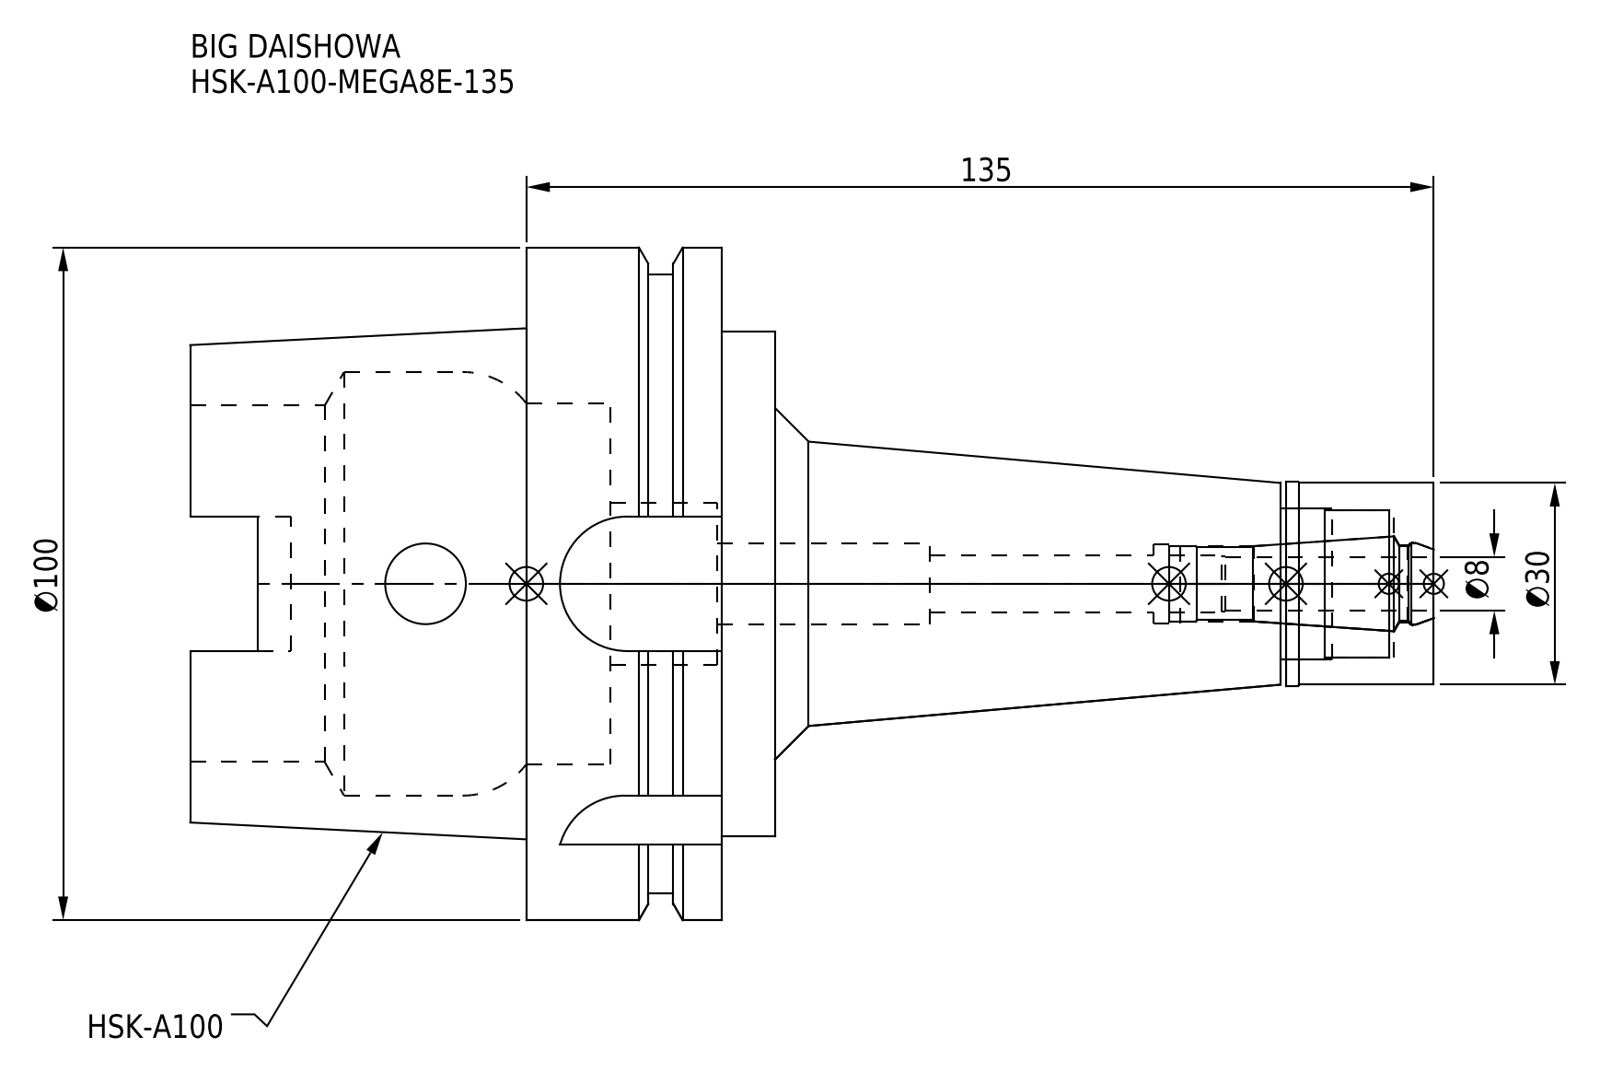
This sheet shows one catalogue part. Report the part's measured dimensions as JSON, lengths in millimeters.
{"part_name": "MEN8_1.stp; DXF_TEMP_ASSY_ASM_4_ASM.stp; HSK-A100-MEGA8E-135-080.stp; HSK-A100-MEGA8E-135 (+3 more)", "step_written_by": "SolidWorks 2019 (CONFIG_CONTROL_DESIGN)", "units": "millimeters", "bodies": {"solids": 2, "faces": 126, "planar": 42, "cylindrical": 56, "other": 28}, "overall_size": [185, 100, 100], "volume_mm3": 376012, "surface_area_mm2": 68520, "round_holes": [[12, 2], [8.4, 1], [11.2, 1], [11.4, 1], [11.8, 1], [12.3, 1], [22, 1], [22.5, 1], [24, 1], [53, 1], [53.8, 1], [63, 1]], "round_bosses_or_shafts": [[100, 1], [92, 1], [75, 1], [30.3, 1], [30, 1]], "partial_cylinders_radius": [[4.88, 4], [10, 4]], "face_to_face_distances": [29, 8, 37, 24.55, 16.55, 12.45, 87, 79, 62.45, 50]}
